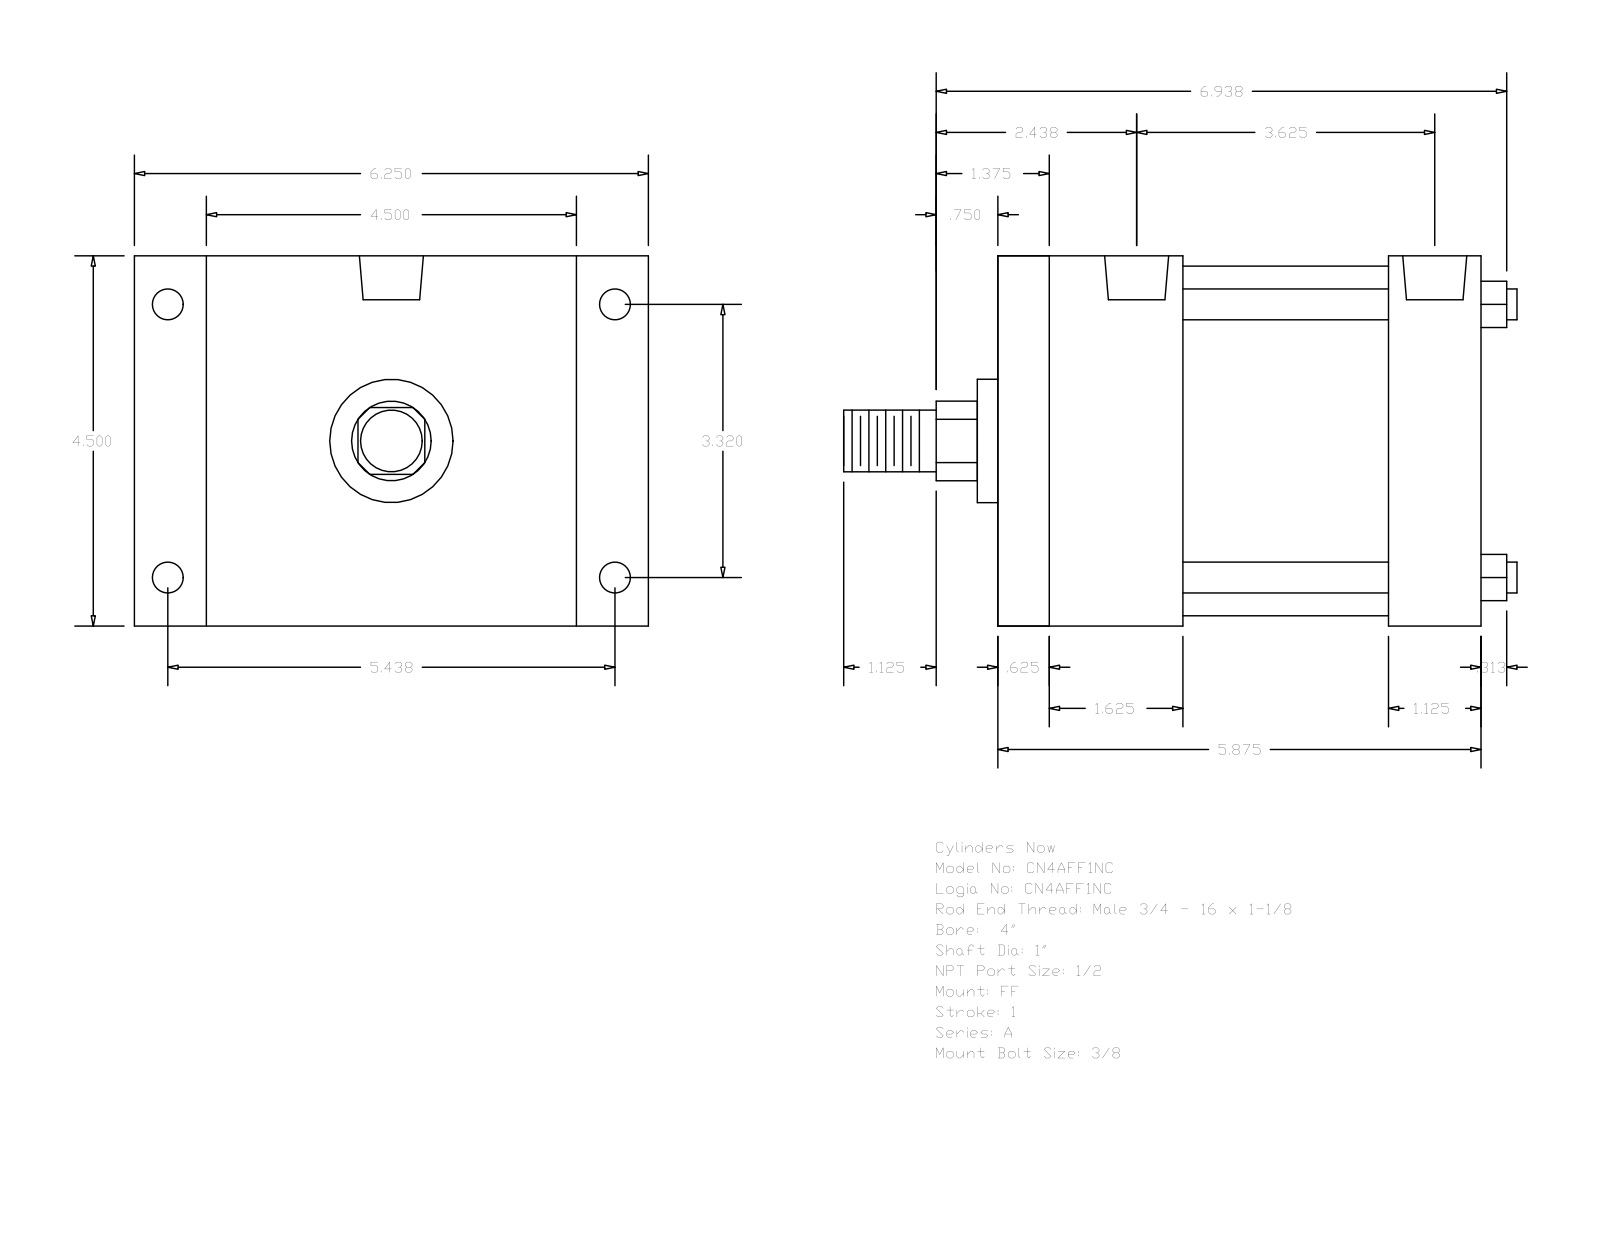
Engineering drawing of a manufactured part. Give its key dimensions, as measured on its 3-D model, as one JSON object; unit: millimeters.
{"part_name": "A_FF__0400_1", "step_written_by": "GSSL Pune (CONFIG_CONTROL_DESIGN)", "units": "millimeters", "bodies": {"solids": 0, "faces": 92, "planar": 64, "cylindrical": 28, "other": 0}, "overall_size": [207.96, 158.75, 114.3], "round_holes": [[8.73, 4], [9.53, 4], [19.77, 2]], "round_bosses_or_shafts": [[9.53, 4], [107.95, 1], [38.1, 1], [25.4, 1], [19.05, 1]], "partial_cylinders_radius": [[12.29, 1]], "face_to_face_distances": [114.3, 149.23, 15.87, 133.36, 63.5, 22.23, 136.53, 120.65, 104.78, 28.58], "hole_center_spacings": [3.18, 84.32, 85.72, 88.9, 138.12, 161.82, 92.08]}
